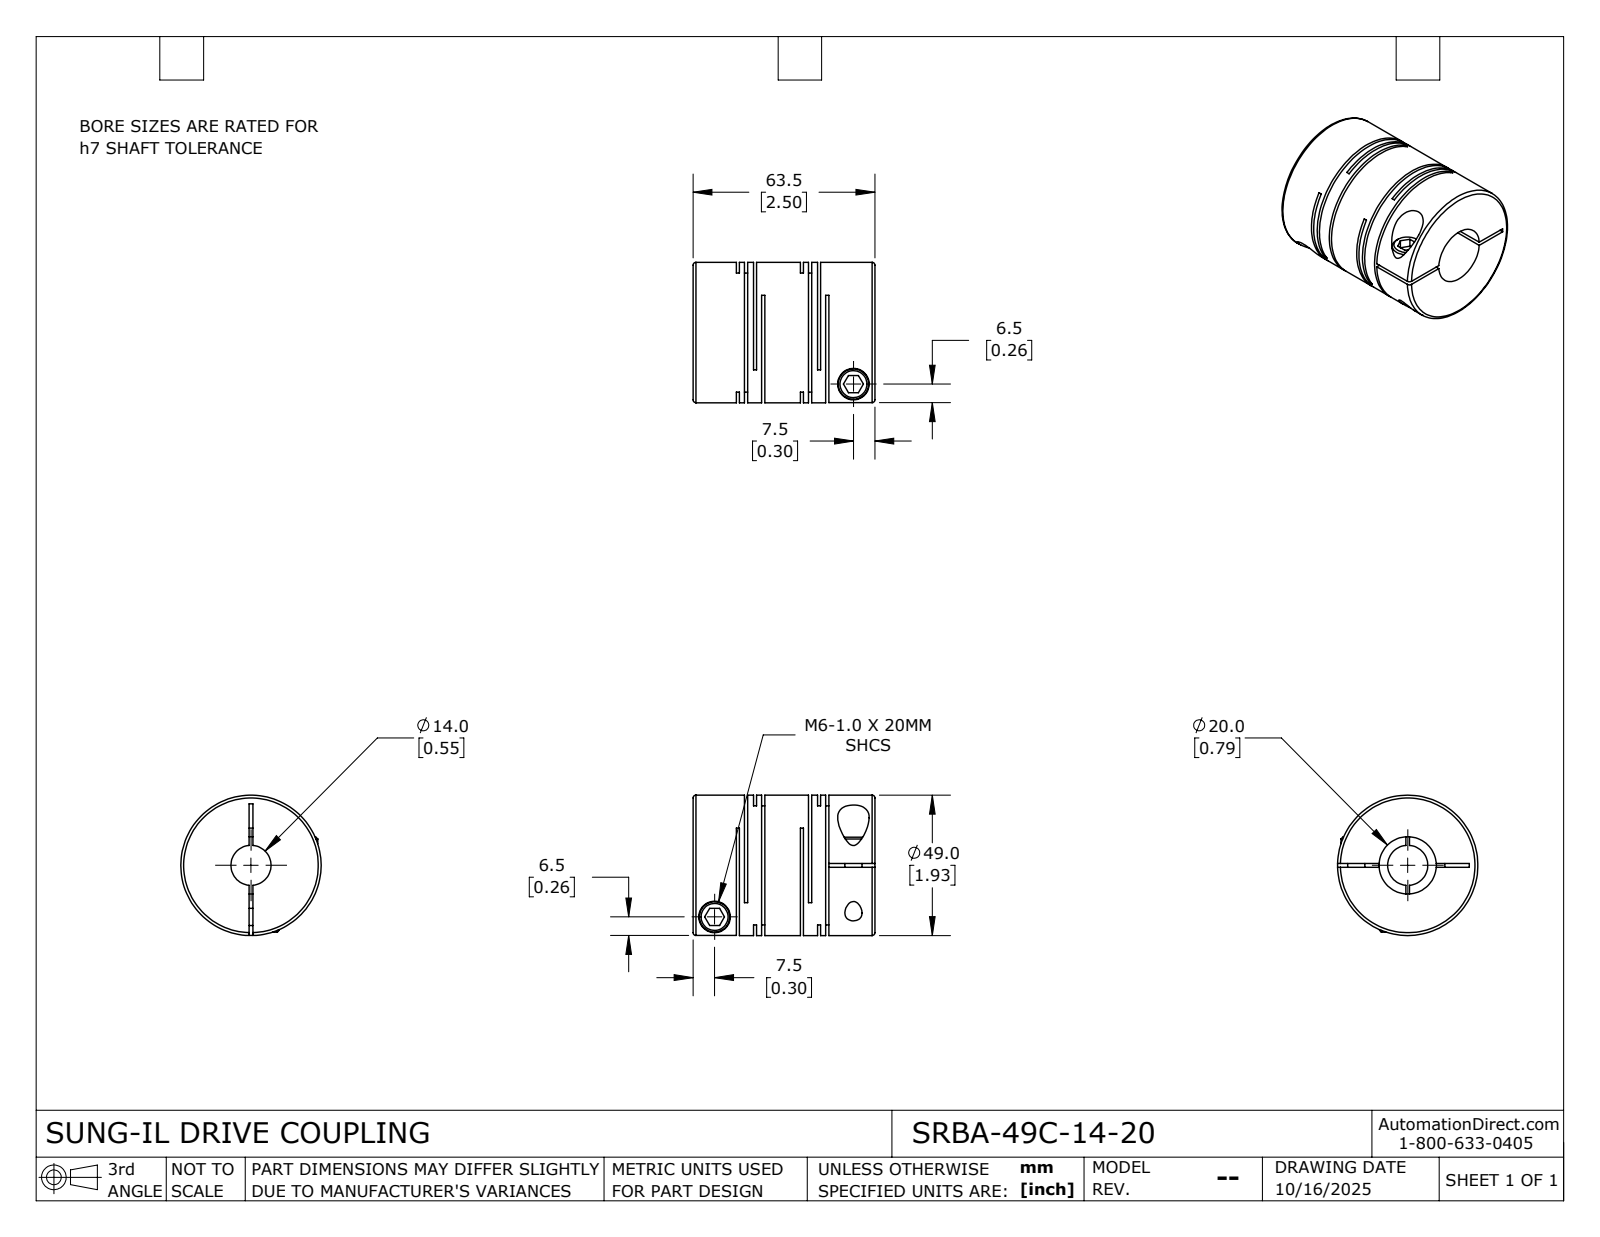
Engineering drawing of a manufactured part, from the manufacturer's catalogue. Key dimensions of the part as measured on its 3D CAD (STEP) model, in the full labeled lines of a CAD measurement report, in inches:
Part name (STEP PRODUCT): SRBA-49C-14-20
STEP written by: SolidWorks 2024 (CONFIG_CONTROL_DESIGN)
Units: inches
Bodies: 1 solid, 115 faces (60 planar, 42 cylindrical, 13 other)
Overall size (bounding box): 2.5 × 1.929 × 1.929
Volume: 5.401 in³ · Surface area: 59.17 in²
Round holes (diameter × count): ⌀0.236 ×2, ⌀0.433 ×2, ⌀0.551 ×1, ⌀0.787 ×1
Round bosses / shafts (diameter × count): ⌀0.417 ×2, ⌀1.929 ×1
Main face-to-face distances: 0.236, 0.043, 0.88, 0.112, 0.837, 0.124, 0.069, 0.193, 0.768, 0.644
